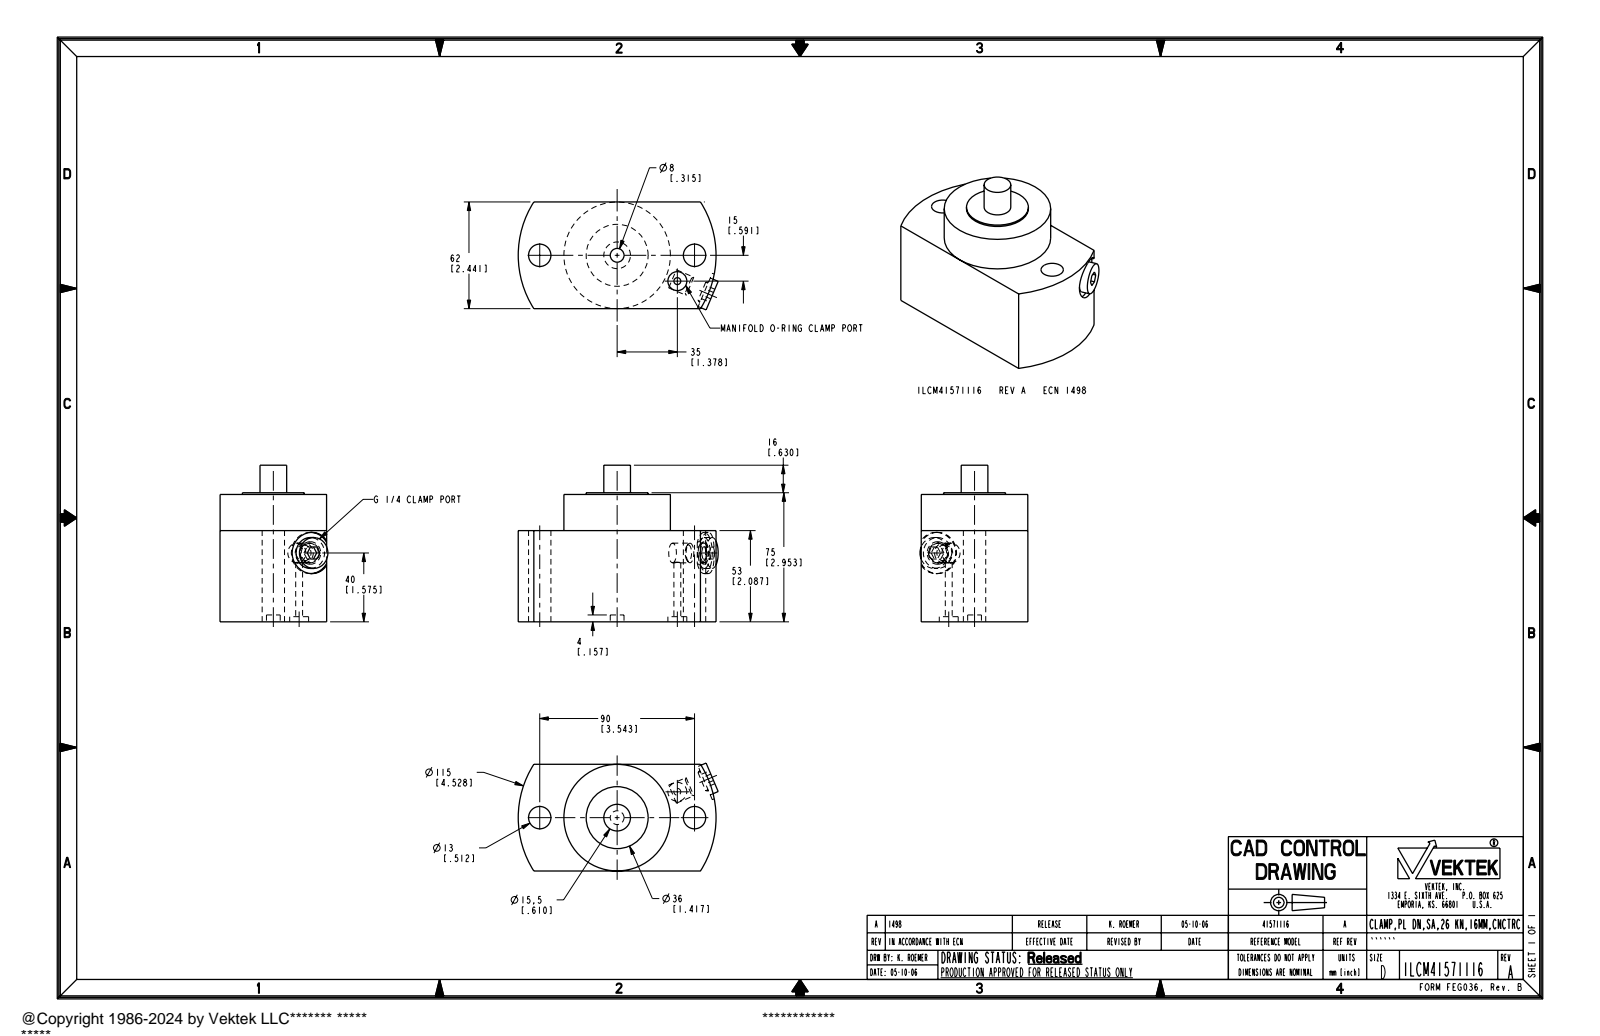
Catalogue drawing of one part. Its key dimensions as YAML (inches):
part_name: "ILCM41571116"
step_written_by: "PRO/ENGINEER BY PARAMETRIC TECHNOLOGY CORPORATION, 2004290 (AUTOMOTIVE_DESIGN_CC2)"
units: inches
bodies: {solids: 1, faces: 52, planar: 21, cylindrical: 27, other: 4}
overall_size: [4.577, 3.583, 2.47]
volume: 25.02
surface_area: 64.12
round_holes:
  - {diameter: 0.512, count: 2}
  - {diameter: 0.157, count: 1}
  - {diameter: 0.315, count: 1}
  - {diameter: 0.433, count: 1}
  - {diameter: 0.451, count: 1}
  - {diameter: 0.945, count: 1}
round_bosses_or_shafts:
  - {diameter: 2.437, count: 1}
  - {diameter: 1.417, count: 1}
  - {diameter: 0.709, count: 1}
  - {diameter: 0.61, count: 1}
  - {diameter: 0.451, count: 1}
partial_cylinders:
  - {radius: 2.264, count: 1}
face_to_face_distances: [2.441, 2.087, 2.913, 0.827, 0.039, 2.953, 0.866, 0.197, 3.583, 1.496]
hole_center_spacings: [1.772, 0.71, 1.499, 3.204, 3.543]
